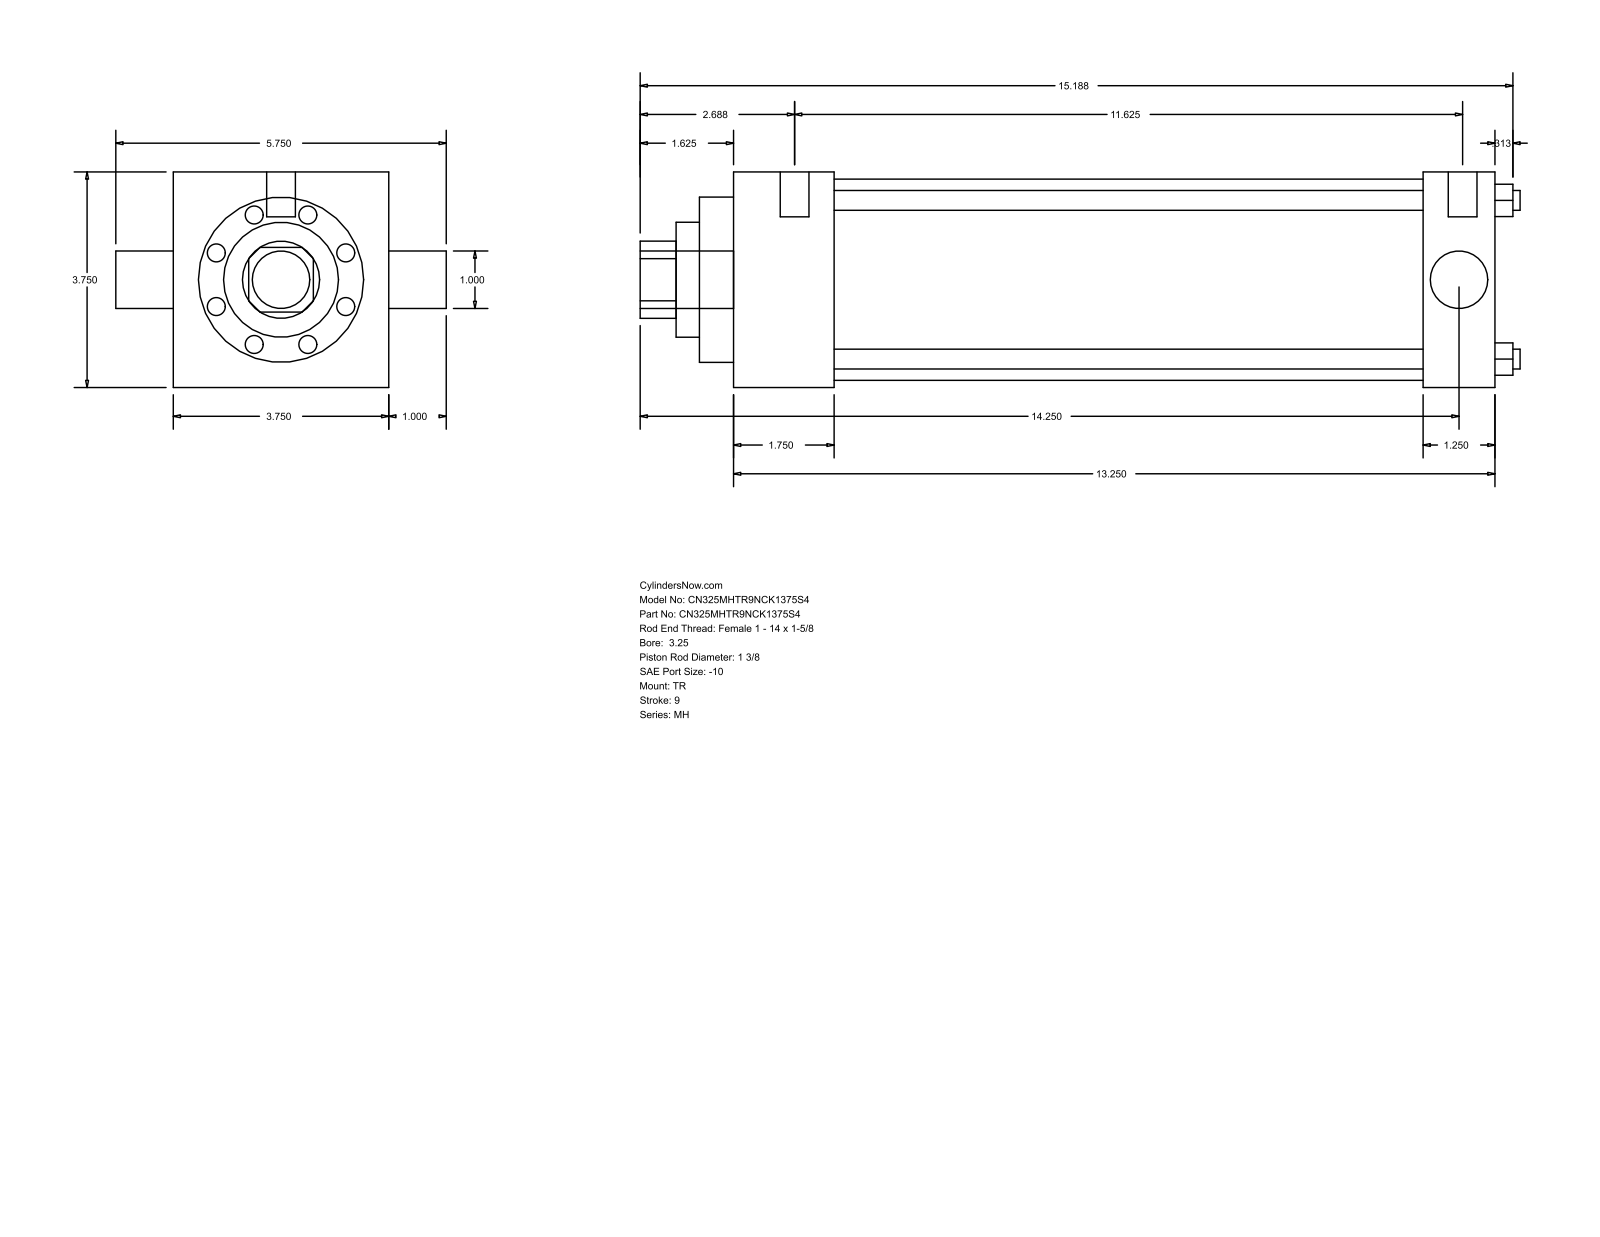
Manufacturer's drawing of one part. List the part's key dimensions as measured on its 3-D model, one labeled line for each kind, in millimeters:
Part name (STEP PRODUCT): MH_TR__0325_1.375
STEP written by: GSSL Pune (CONFIG_CONTROL_DESIGN)
Units: millimetres
Bodies: 0 solids, 86 faces (61 planar, 25 cylindrical, 0 other)
Overall size (bounding box): 388.94 × 146.05 × 95.25
Round holes (diameter × count): ⌀8.76 ×4, ⌀25.4 ×1, ⌀34.92 ×1, ⌀50.8 ×1, ⌀73.03 ×1, ⌀88.9 ×1
Round bosses / shafts (diameter × count): ⌀5.56 ×3, ⌀12.7 ×2, ⌀25.4 ×1
Partial cylindrical surfaces — rounded edges, fillets, slot ends (radius × count): R17.06 ×1
Main face-to-face distances: 95.24, 336.55, 44.45, 304.8, 260.35, 292.1, 31.75, 15.08, 59.53, 319.88
Hole centre spacings: 49.57, 70.1, 99.14
